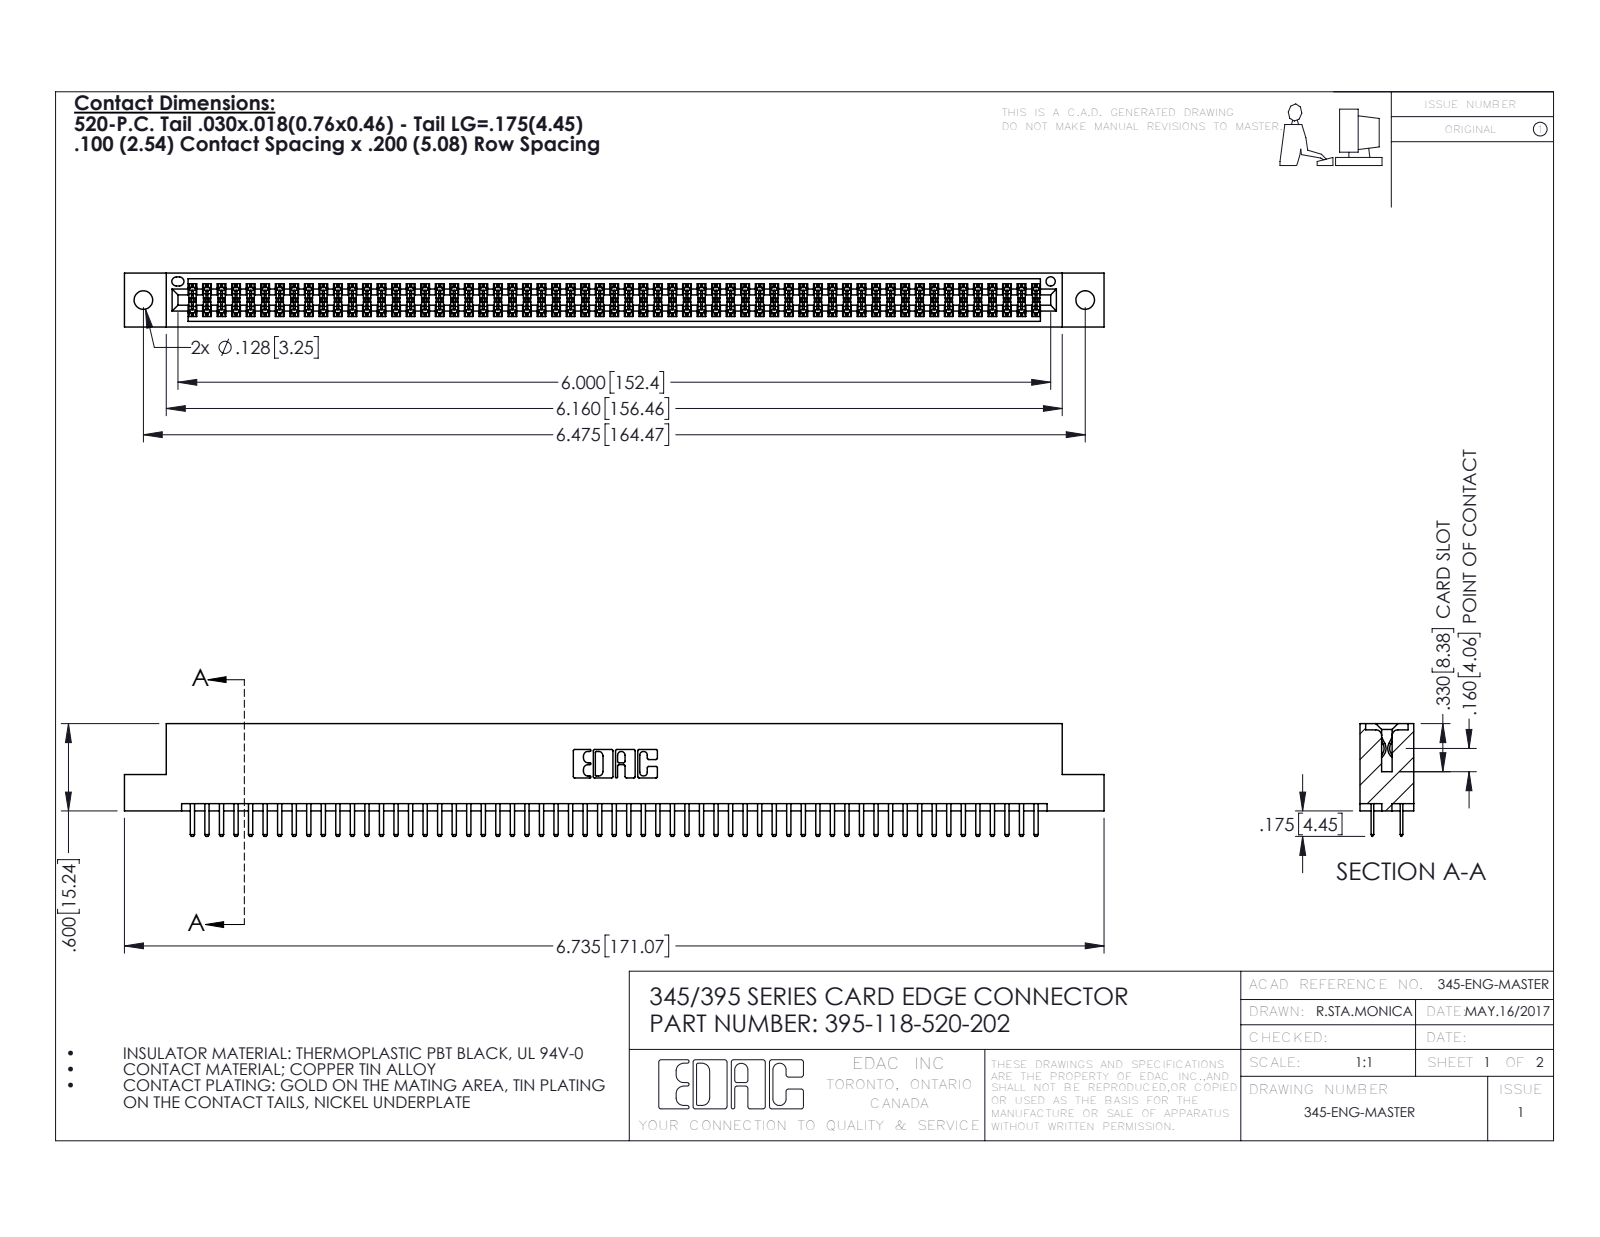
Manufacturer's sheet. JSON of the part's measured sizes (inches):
{"part_name": "345-292-001_345-293-120; 395-118-520-202; 345 Part_Flush Mounting Lugs - 0.128 Dia", "step_written_by": "SolidWorks 2016 (CONFIG_CONTROL_DESIGN)", "units": "inches", "bodies": {"solids": 119, "faces": 6498, "planar": 4210, "cylindrical": 2288, "other": 0}, "overall_size": [6.735, 0.775, 0.37], "volume_in3": 1.018, "surface_area_in2": 38.15, "round_holes": [[0.128, 2], [0.064, 1]], "partial_cylinders_radius": [[0.006, 177], [0.01, 122], [0.01, 22], [0.007, 6], [0.031, 6], [0.026, 3], [0.014, 2], [0.019, 2]], "face_to_face_distances": [0.298, 0.072, 0.2, 0.37, 0.098, 0.272, 0.025, 0.225, 0.022, 0.072], "hole_center_spacings": [0.27, 6.239, 6.475]}
